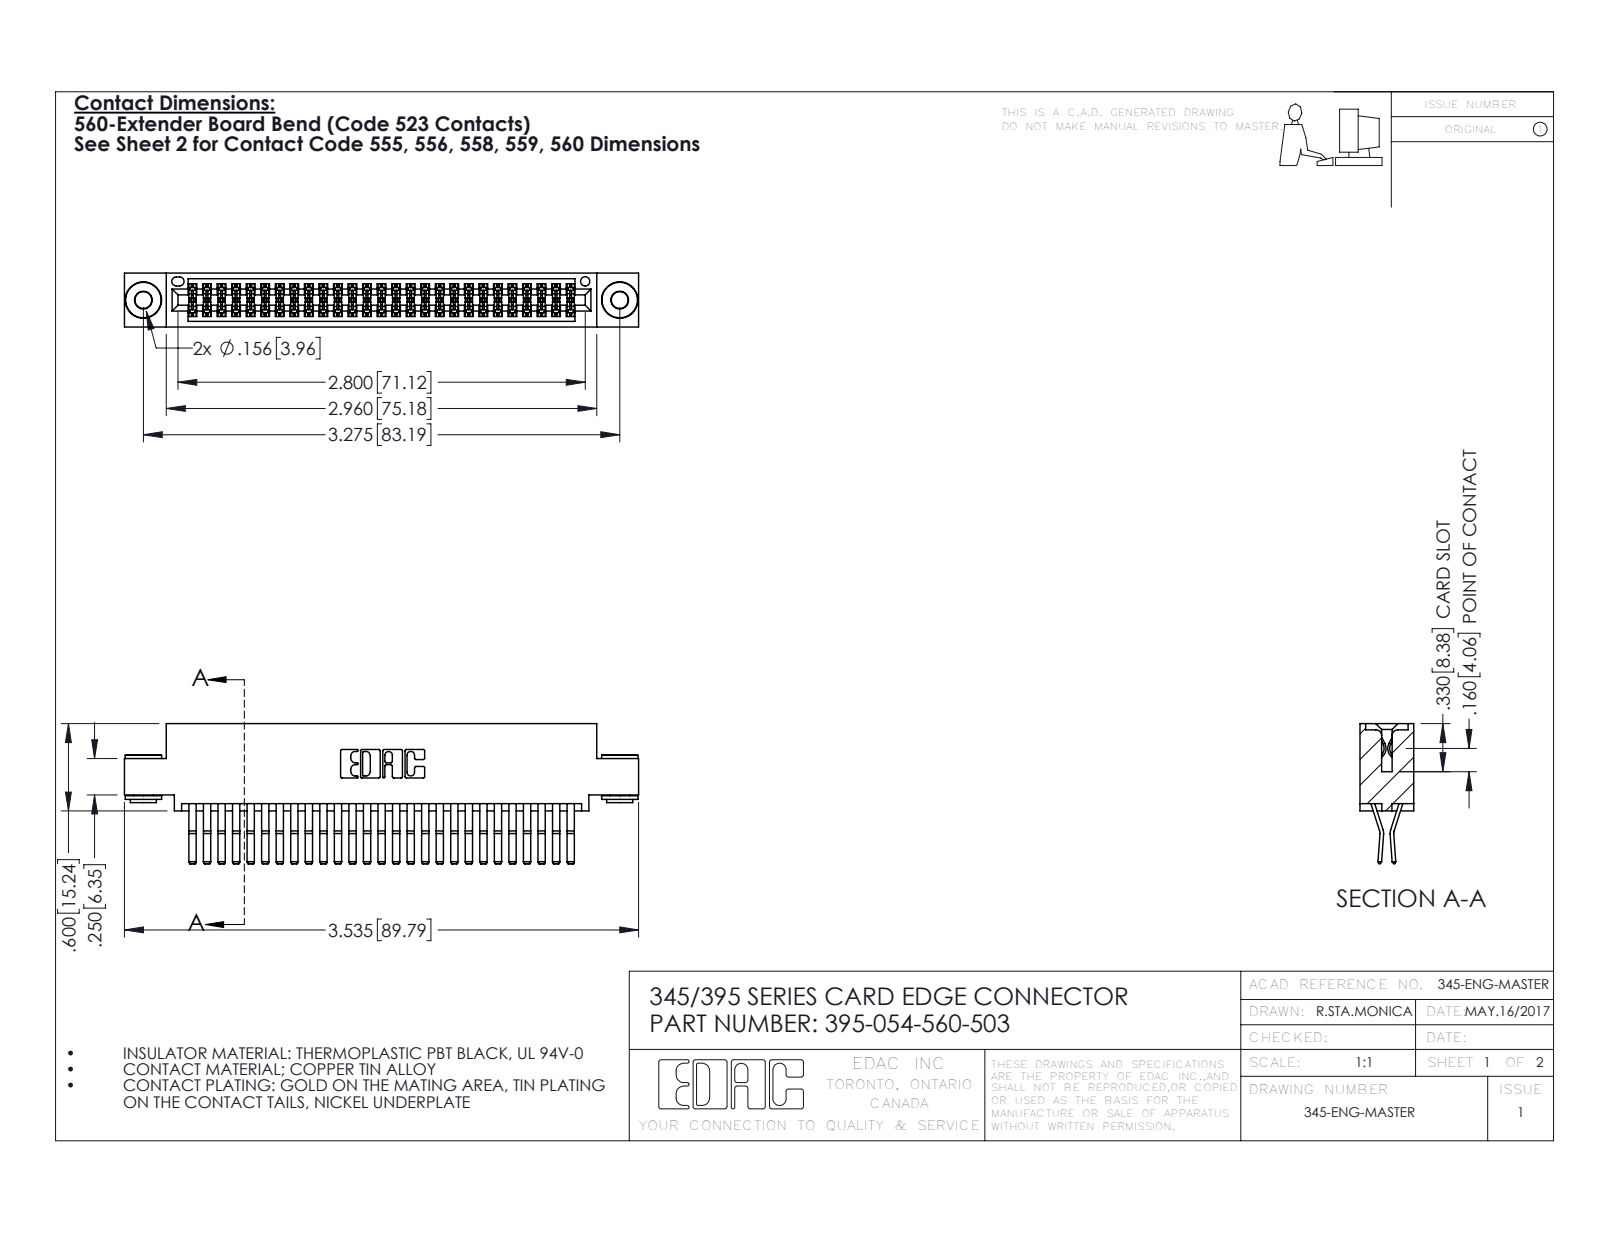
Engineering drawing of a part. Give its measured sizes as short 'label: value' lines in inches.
name: 345 Part_0.110 Offset - 0.156 Dia-TH; 345-292-001_560 Tail; 345-250-002_345-250-002-102; 395-054-560-503
written by: SolidWorks 2016 (CONFIG_CONTROL_DESIGN)
unit: in
bodies: 57 solids, 2976 faces (1876 planar, 1092 cylindrical, 8 other)
size: 3.535 × 0.962 × 0.37
volume: 0.542 in³; area: 21.77 in²
holes: 2× ⌀0.116, 2× ⌀0.156, 1× ⌀0.064
bosses: 2× ⌀0.25, 2× ⌀0.18, 2× ⌀0.136
rounds: 81× R0.006, 22× R0.01, 6× R0.007, 6× R0.031, 3× R0.026, 2× R0.01, 2× R0.014, 2× R0.019
face distances: 0.025, 0.072, 0.298, 0.37, 0.2, 0.098, 0.272, 0.225, 0.175, 0.149
hole spacings: 0.27, 3.04, 3.275
